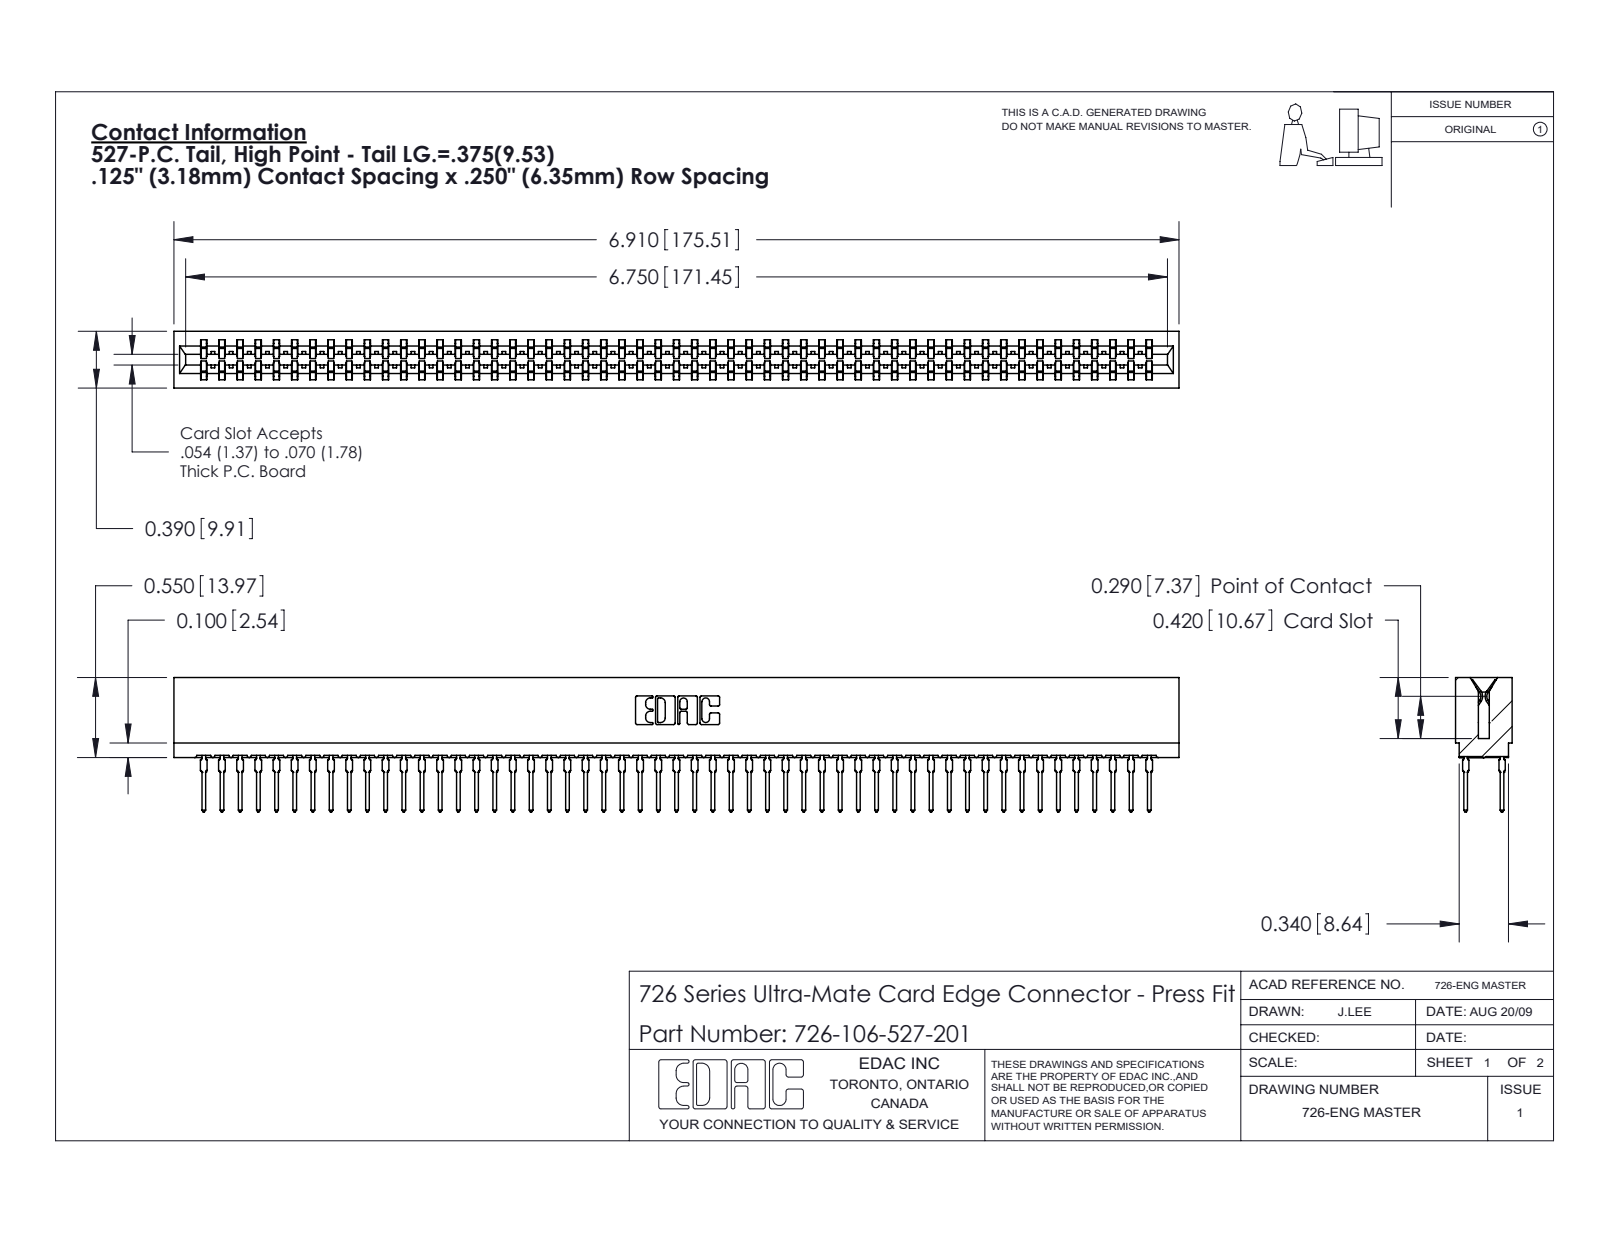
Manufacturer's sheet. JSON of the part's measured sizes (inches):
{"part_name": "726 Part_.515 Slot Depth - 01; 726-106-527-201; 746-292-001_527", "step_written_by": "SolidWorks 2020 (CONFIG_CONTROL_DESIGN)", "units": "inches", "bodies": {"solids": 107, "faces": 9584, "planar": 4931, "cylindrical": 1897, "other": 2756}, "overall_size": [6.91, 0.924, 0.39], "volume_in3": 0.993, "surface_area_in2": 43.62, "partial_cylinders_radius": [[0.021, 212], [0.015, 54], [0.01, 22], [0.005, 8], [0.011, 8], [0.007, 6], [0.031, 6], [0.026, 3]], "face_to_face_distances": [0.057, 0.333, 0.025, 0.307, 0.39, 0.25, 0.275, 0.083, 0.365, 0.032]}
